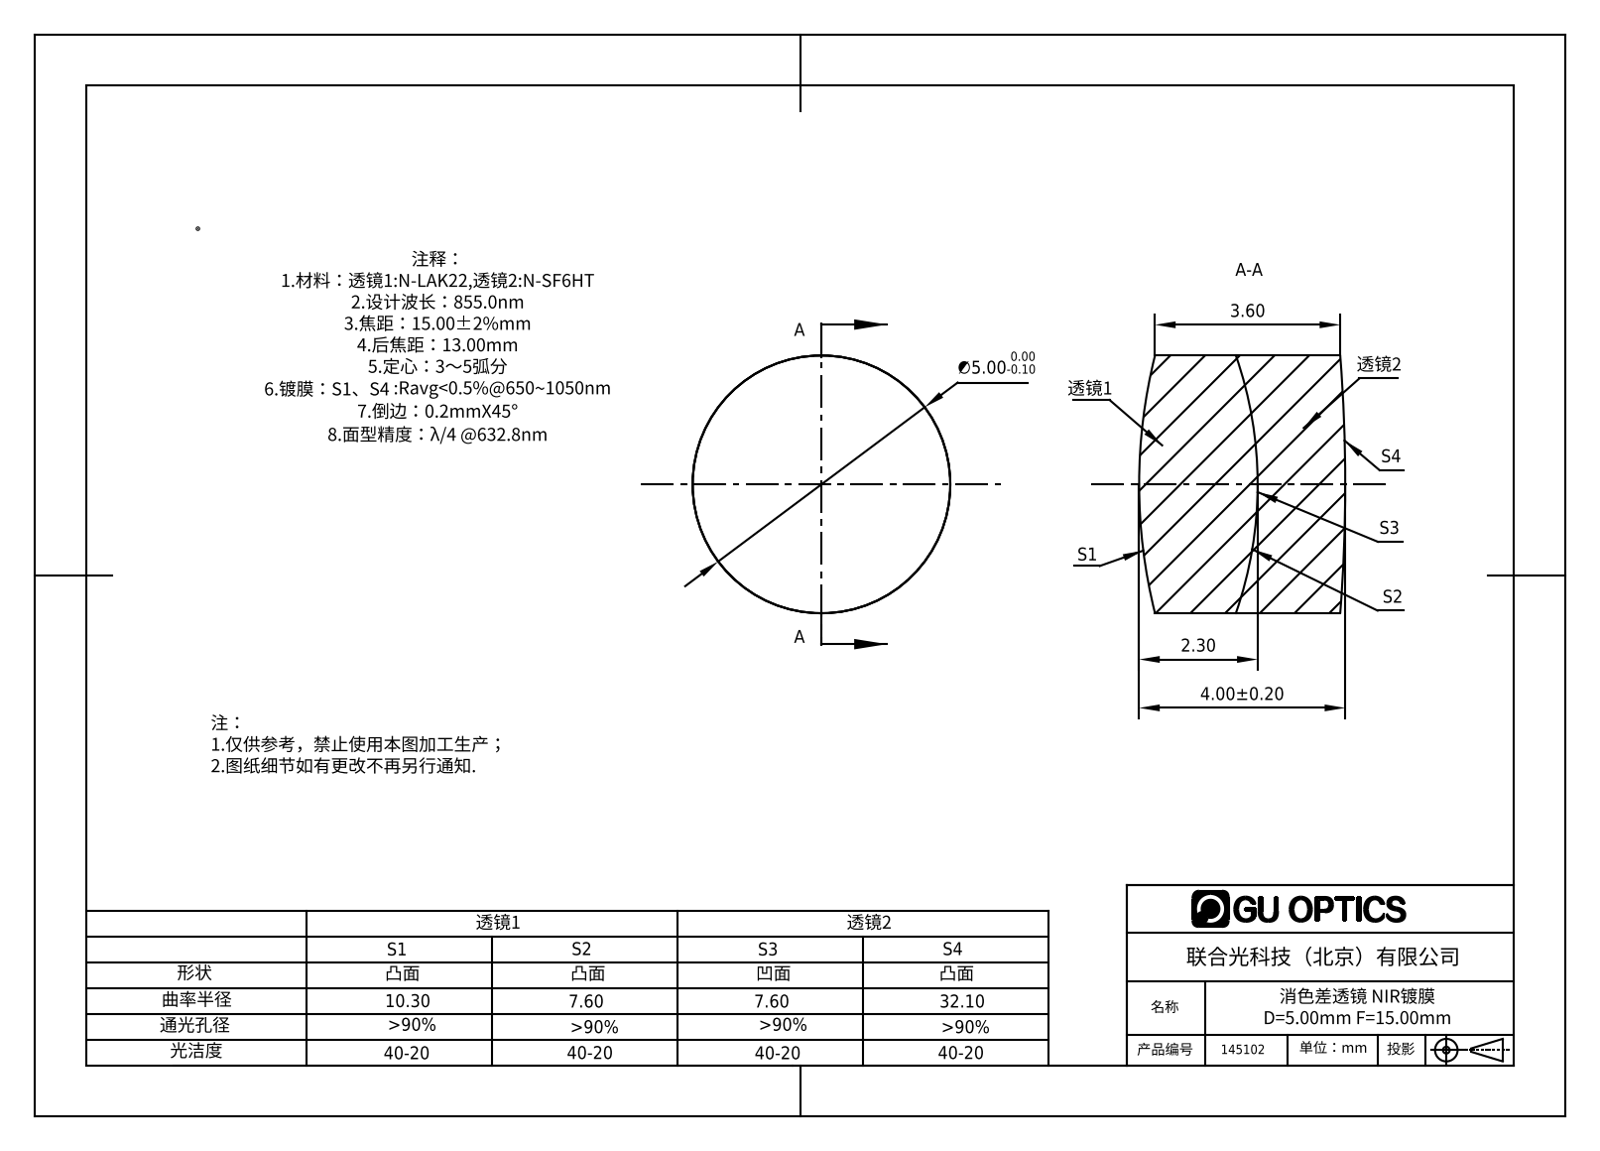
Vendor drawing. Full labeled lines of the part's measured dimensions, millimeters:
Part name (STEP PRODUCT): 145102
STEP written by: SolidWorks 2016 (AUTOMOTIVE_DESIGN)
Units: millimetres
Bodies: 2 solids, 12 faces (0 planar, 4 cylindrical, 8 other)
Overall size (bounding box): 5 × 5 × 4
Volume: 75 mm³ · Surface area: 136 mm²
Round bosses / shafts (diameter × count): ⌀5 ×1
